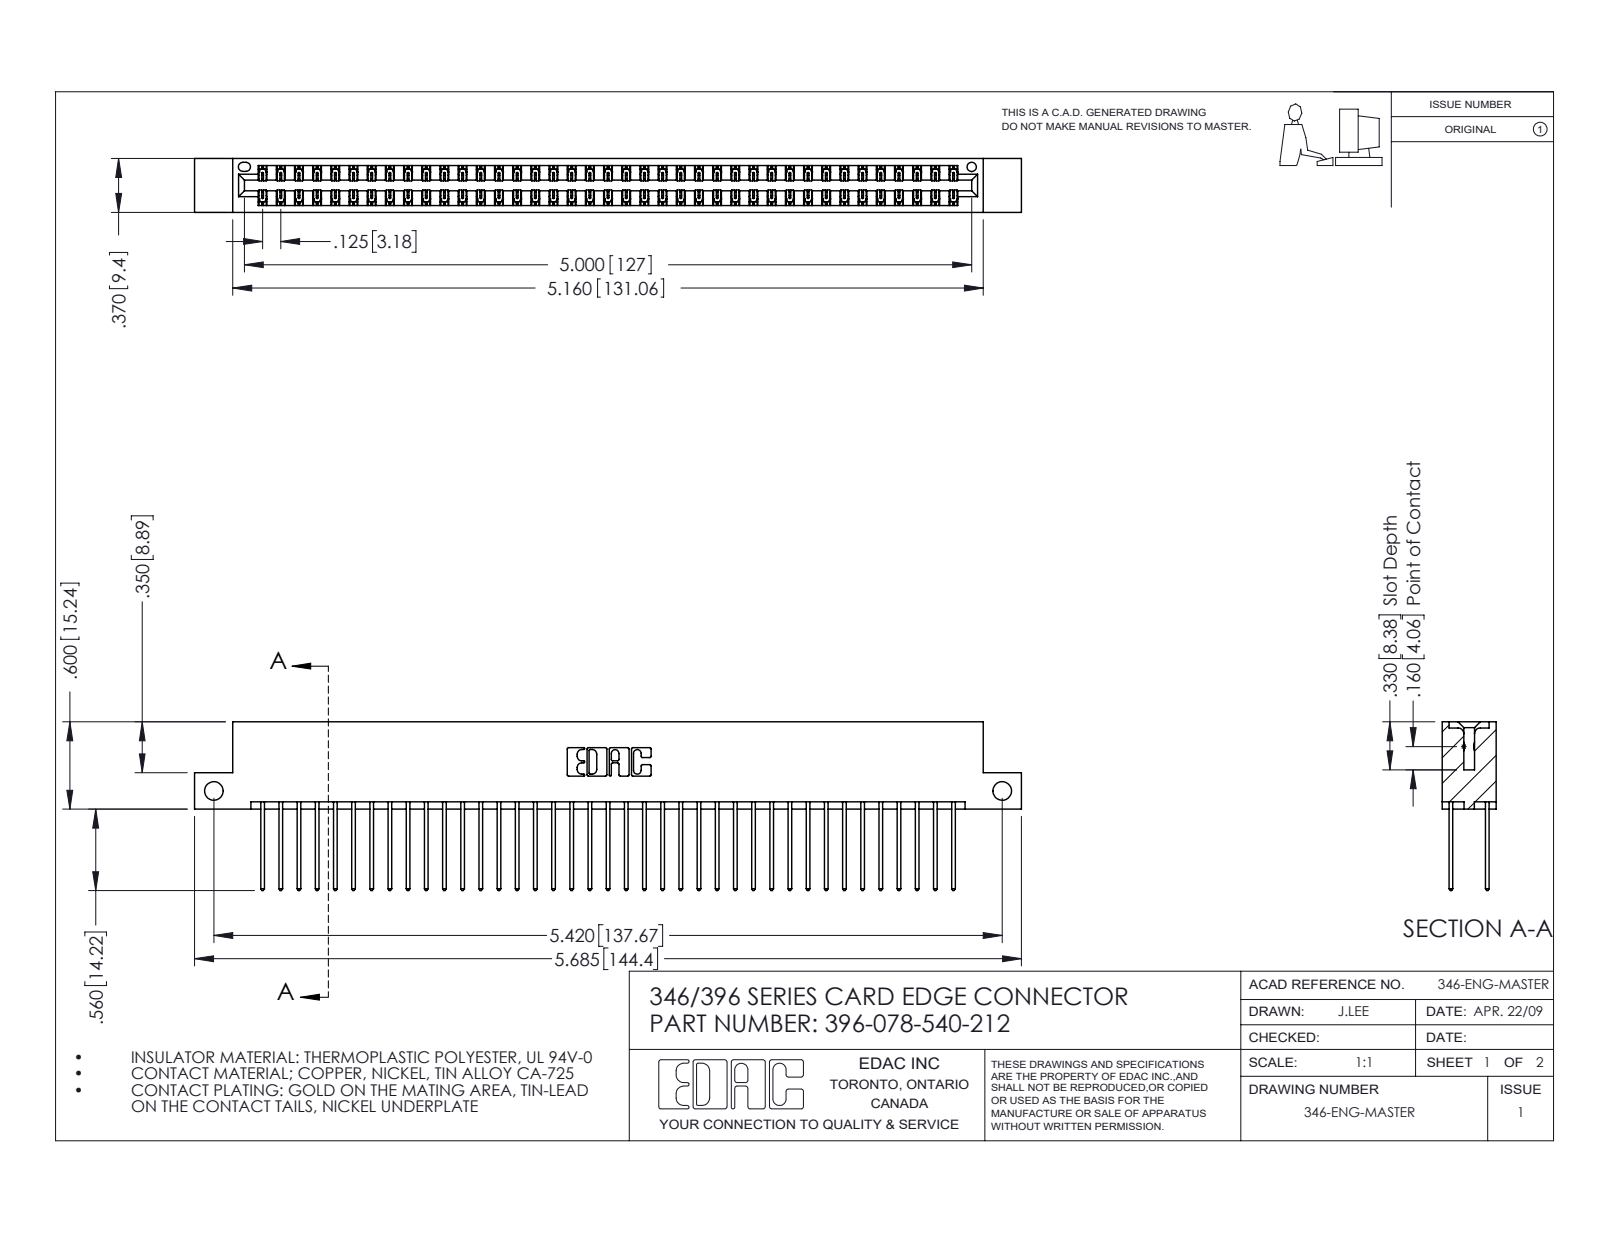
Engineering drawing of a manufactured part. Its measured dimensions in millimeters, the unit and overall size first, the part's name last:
Units: millimetres
Overall size (bounding box): 144.4 × 29.5 × 9.4
Round holes (diameter × count): ⌀3.3 ×2, ⌀1.6 ×1
Partial cylindrical surfaces — rounded edges, fillets, slot ends (radius × count): R0.2 ×117, R0.3 ×78, R0.3 ×22, R0.2 ×6, R0.8 ×6, R0.7 ×3, R0.4 ×2, R0.6 ×2
Main face-to-face distances: 1.2, 8.2, 6.4, 1.8, 7.6, 0.6, 9.4, 7, 3.8, 5.6
Hole centre spacings: 137.7
Volume: 14 300 mm³ · Surface area: 20 830 mm²
Bodies: 79 solids, 4178 faces (2806 planar, 1372 cylindrical, 0 other)
Part name (STEP PRODUCT): 345-292-001_345-293-140; 346 Part_Flush Mounting Lugs - Side Mount; 396-078-540-212
STEP written by: SolidWorks 2016 (CONFIG_CONTROL_DESIGN)
